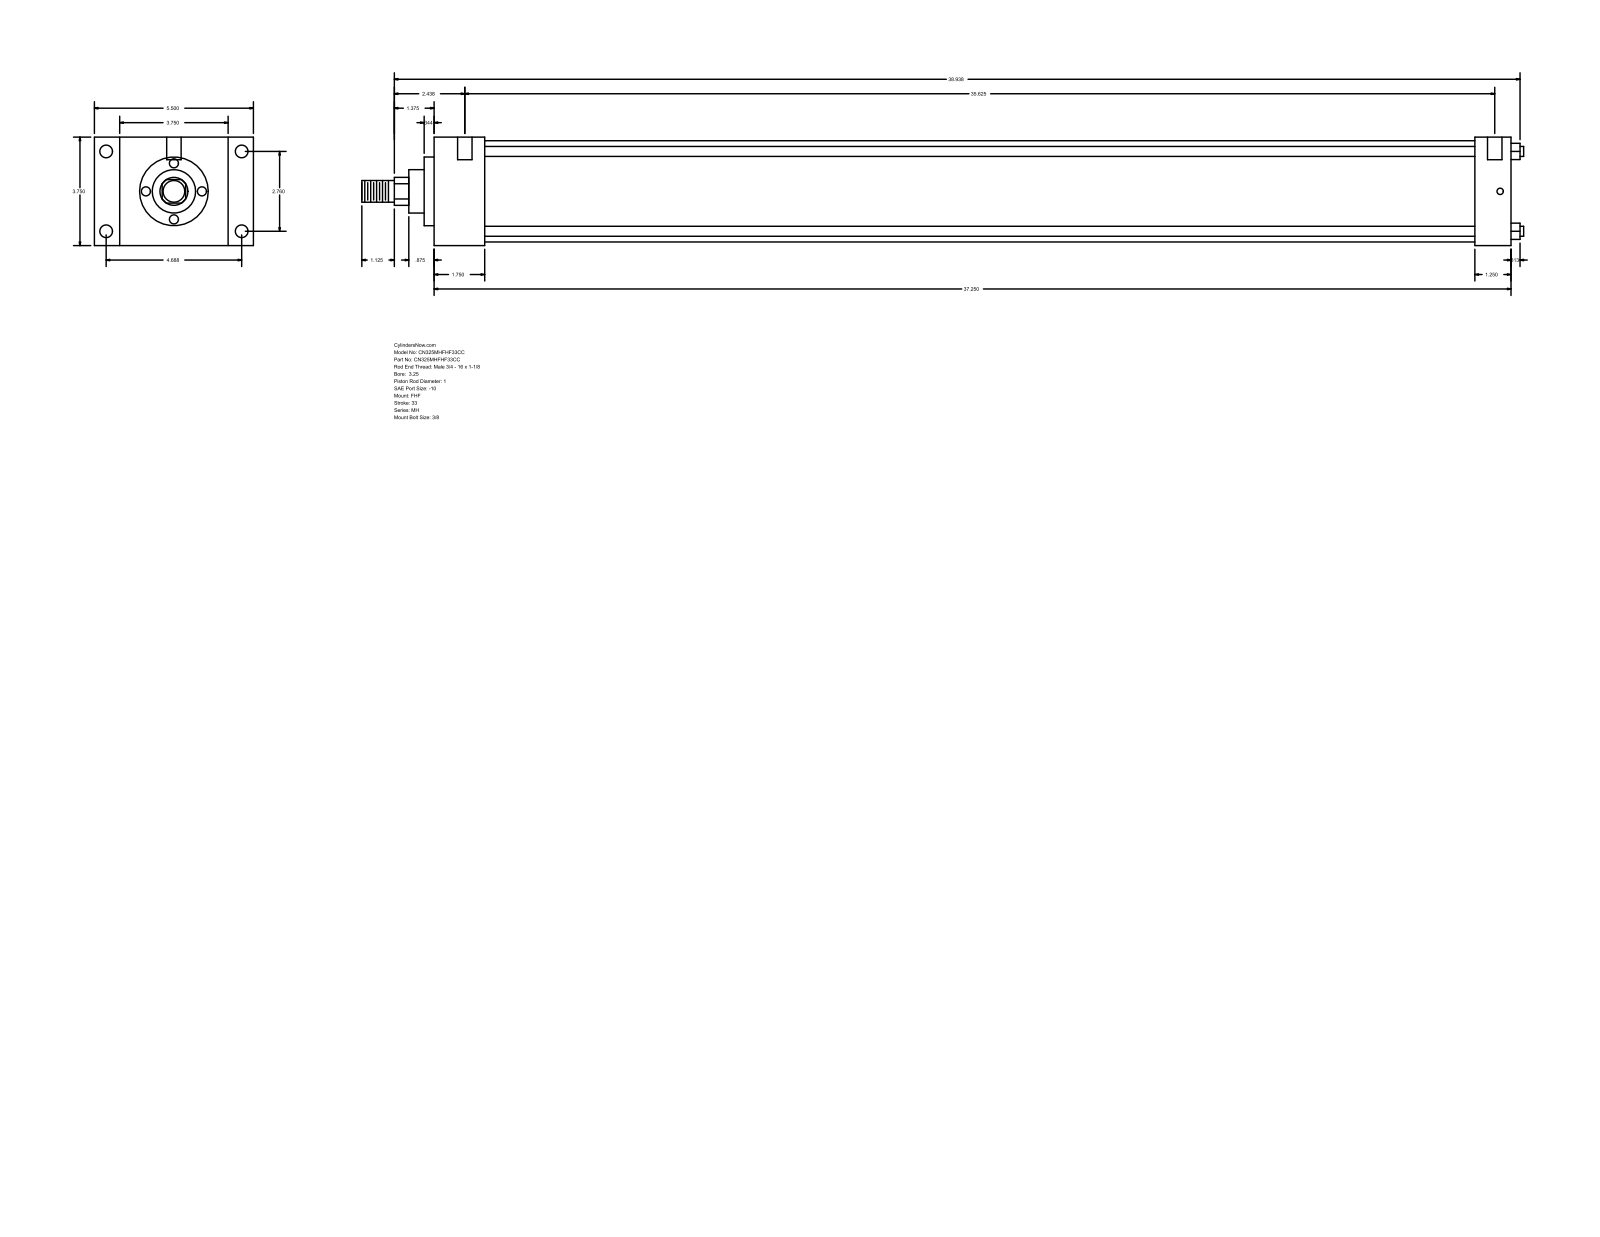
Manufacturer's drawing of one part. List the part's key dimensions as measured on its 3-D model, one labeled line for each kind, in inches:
Part name (STEP PRODUCT): MH_FHF__0325_1
STEP written by: GSSL Pune (CONFIG_CONTROL_DESIGN)
Units: inches
Bodies: 0 solids, 90 faces (61 planar, 29 cylindrical, 0 other)
Overall size (bounding box): 40.187 × 5.5 × 3.75
Round holes (diameter × count): ⌀0.219 ×4, ⌀0.438 ×4, ⌀0.5 ×2
Round bosses / shafts (diameter × count): ⌀0.345 ×4, ⌀3.5 ×1, ⌀2.375 ×1, ⌀1.5 ×1, ⌀1 ×1, ⌀0.75 ×1
Partial cylindrical surfaces — rounded edges, fillets, slot ends (radius × count): R0.484 ×1
Main face-to-face distances: 3.75, 37.25, 1.75, 35.5, 0.875, 4.625, 5.5, 36, 34.25, 1.25
Hole centre spacings: 2.76, 4.687, 5.439, 35.875, 0.062, 0.187, 35.625, 35.687
